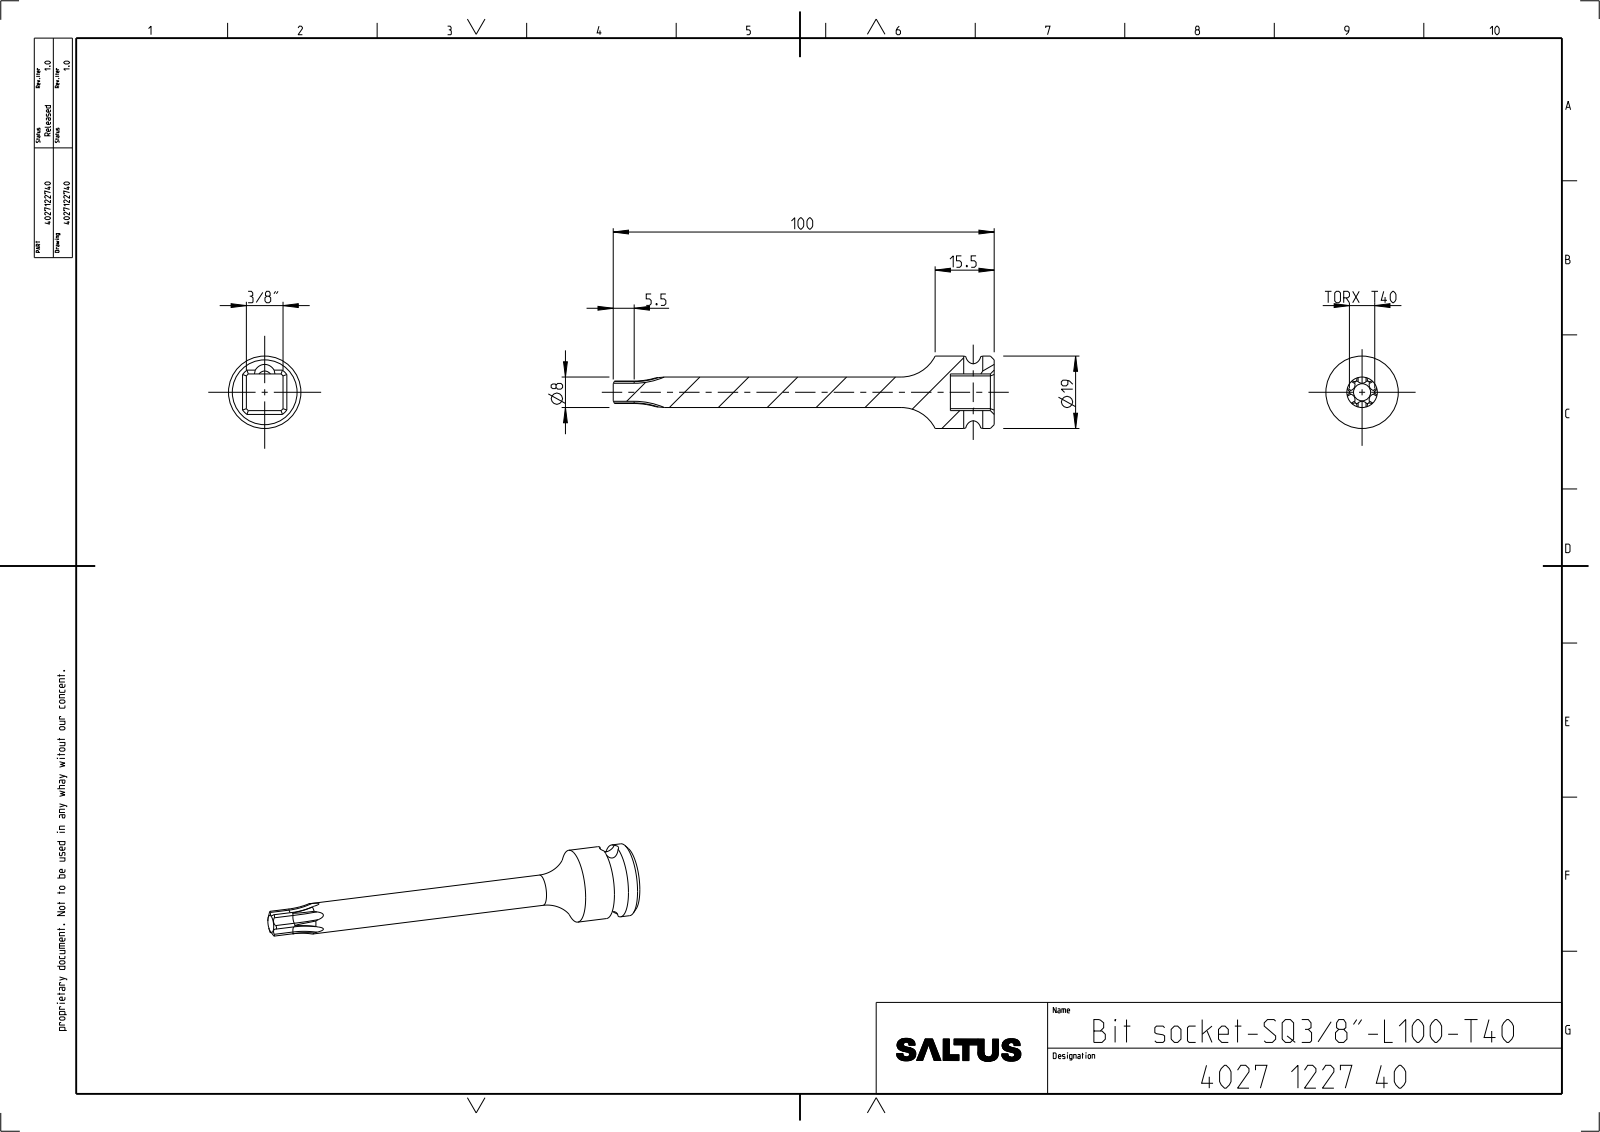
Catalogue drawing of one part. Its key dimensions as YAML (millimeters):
part_name: "4027122740"
step_written_by: "CREO PARAMETRIC BY PTC INC, 2022414 (CONFIG_CONTROL_DESIGN)"
units: millimeters
bodies: {solids: 1, faces: 81, planar: 12, cylindrical: 33, other: 36}
overall_size: [100, 19, 19]
volume: 7339
surface_area: 3973
round_holes:
  - {diameter: 5, count: 1}
round_bosses_or_shafts:
  - {diameter: 19, count: 1}
  - {diameter: 8, count: 1}
partial_cylinders:
  - {radius: 0.51, count: 6}
  - {radius: 1.47, count: 6}
  - {radius: 3, count: 1}
  - {radius: 3.33, count: 1}
  - {radius: 6.45, count: 1}
face_to_face_distances: [9.62, 11.5, 100, 88.5]
